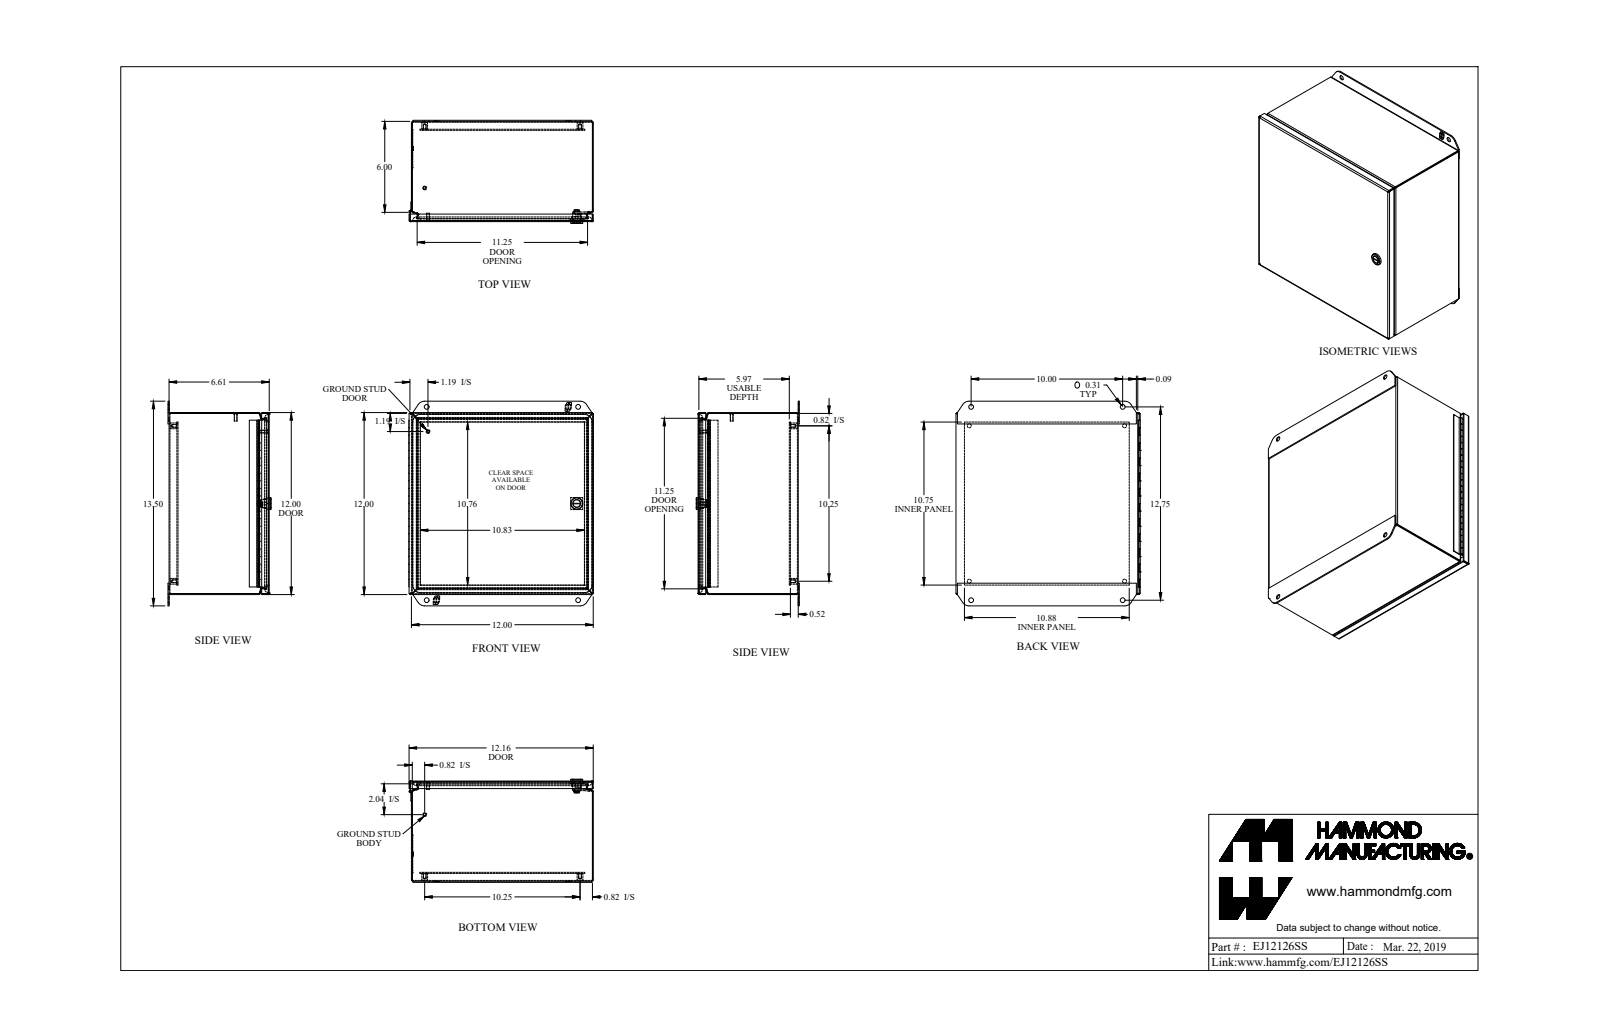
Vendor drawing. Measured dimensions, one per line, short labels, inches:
name: EJ12126SS_Default
written by: SolidWorks 2019 (CONFIG_CONTROL_DESIGN)
unit: in
bodies: 16 solids, 720 faces (402 planar, 222 cylindrical, 96 other)
size: 13.5 × 12.165 × 6.805
volume: 51.78 in³; area: 1 710 in²
holes: 4× ⌀0.156, 4× ⌀0.265, 4× ⌀0.313, 1× ⌀0.05, 1× ⌀0.516
bosses: 4× ⌀0.375, 2× ⌀0.25, 2× ⌀0.19, 1× ⌀0.788, 1× ⌀0.535, 1× ⌀0.496, 1× ⌀0.435, 1× ⌀0.1
rounds: 16× R0.029, 16× R0.086, 12× R0.281, 4× R0.25, 4× R0.499, 4× R0.5, 2× R0.06, 1× R0.03
face distances: 0.057, 6.554, 11.943, 0.072, 0.589, 12, 11.886, 6.611, 6.497, 6.094
hole spacings: 1.256, 10.202, 10.25, 11.501, 15.322, 5.13, 6.376, 10
